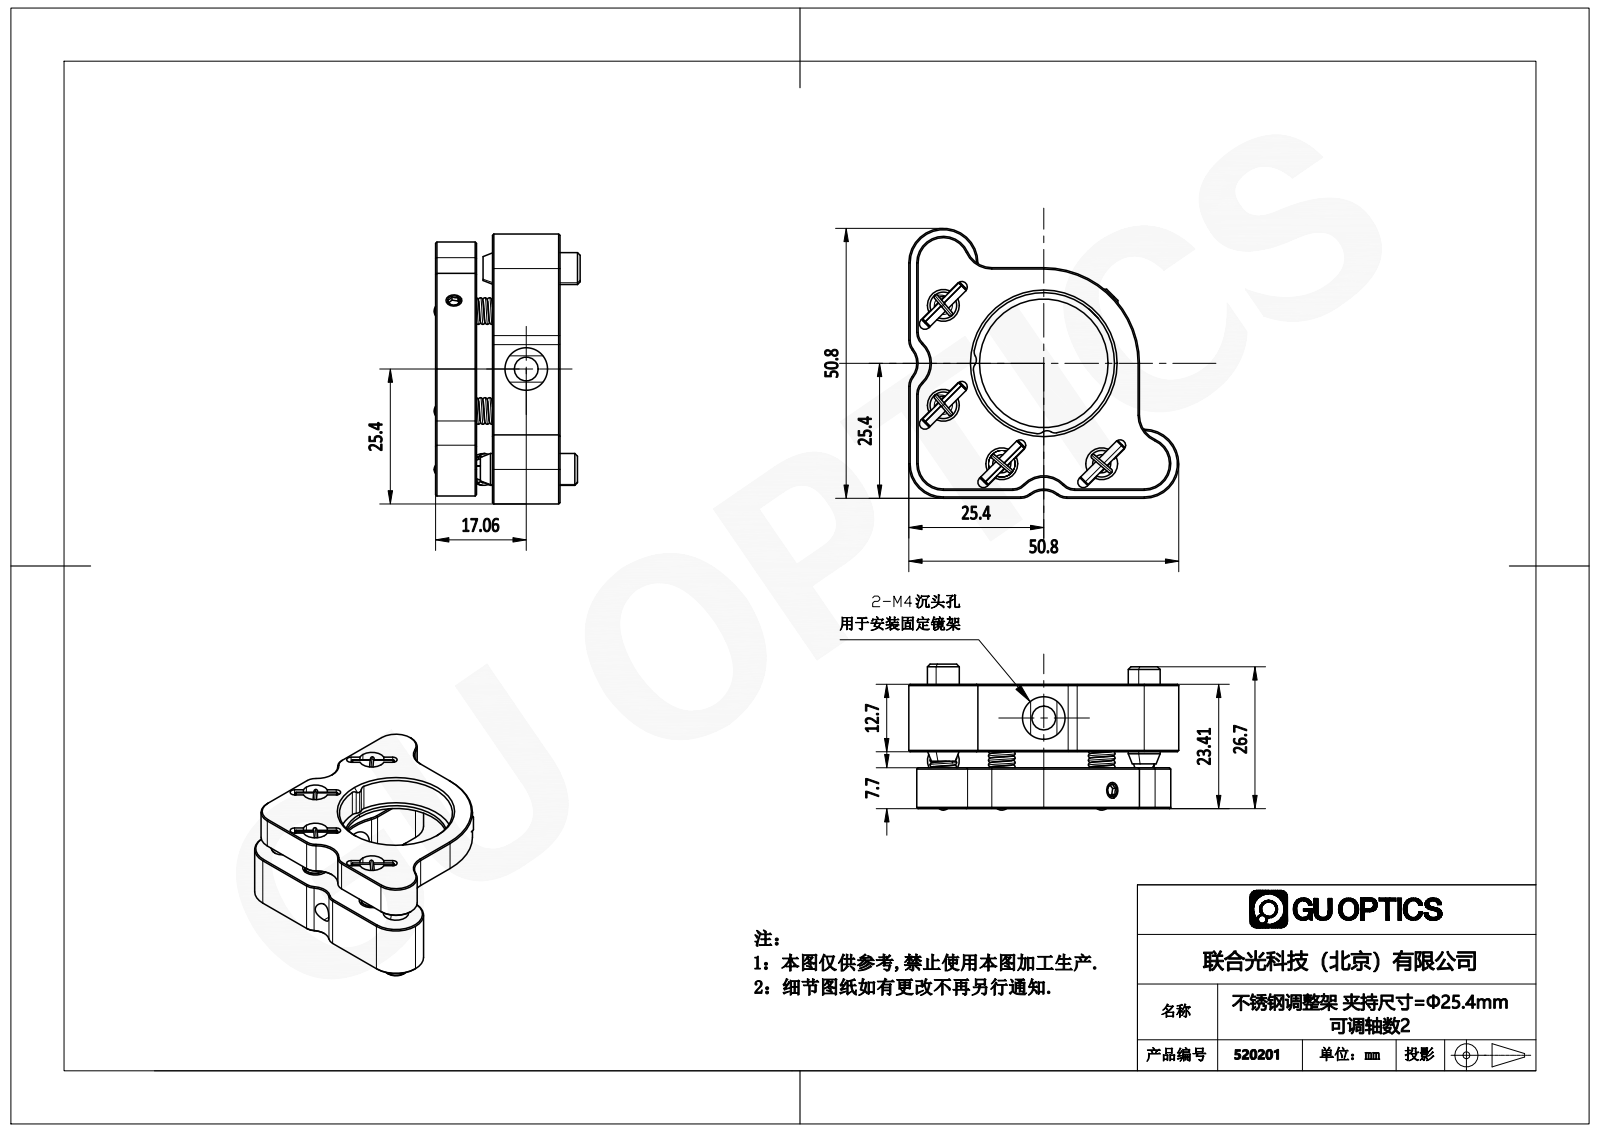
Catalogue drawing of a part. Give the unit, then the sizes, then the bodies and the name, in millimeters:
Units: millimetres
Overall size (bounding box): 50.8 × 50.8 × 27.47
Round holes (diameter × count): ⌀6 ×4, ⌀4.5 ×2, ⌀8 ×2, ⌀3.3 ×1, ⌀24.2 ×1, ⌀26.6 ×1
Round bosses / shafts (diameter × count): ⌀2 ×8, ⌀6 ×2, ⌀1.5 ×2, ⌀3 ×1
Partial cylindrical surfaces — rounded edges, fillets, slot ends (radius × count): R5 ×9, R1.05 ×8, R3 ×8, R1.5 ×6, R6.5 ×3, R0.78 ×2, R4 ×2, R13.5 ×1
Main face-to-face distances: 7.7, 3.01, 10.71, 12.7, 15.71, 23.41, 1.5, 13, 11.5, 43.4
Hole centre spacings: 18.8, 20.48, 21.82, 31.77, 15.56, 42.14
Bodies: 0 solids, 403 faces (132 planar, 118 cylindrical, 153 other)
Part name (STEP PRODUCT): 1.1.19.13_ZJD-1.0-2_经济型不锈钢光学调整架，用于1英寸光学元件，两轴，M4螺孔
STEP written by: SolidWorks 2018 (AUTOMOTIVE_DESIGN)
